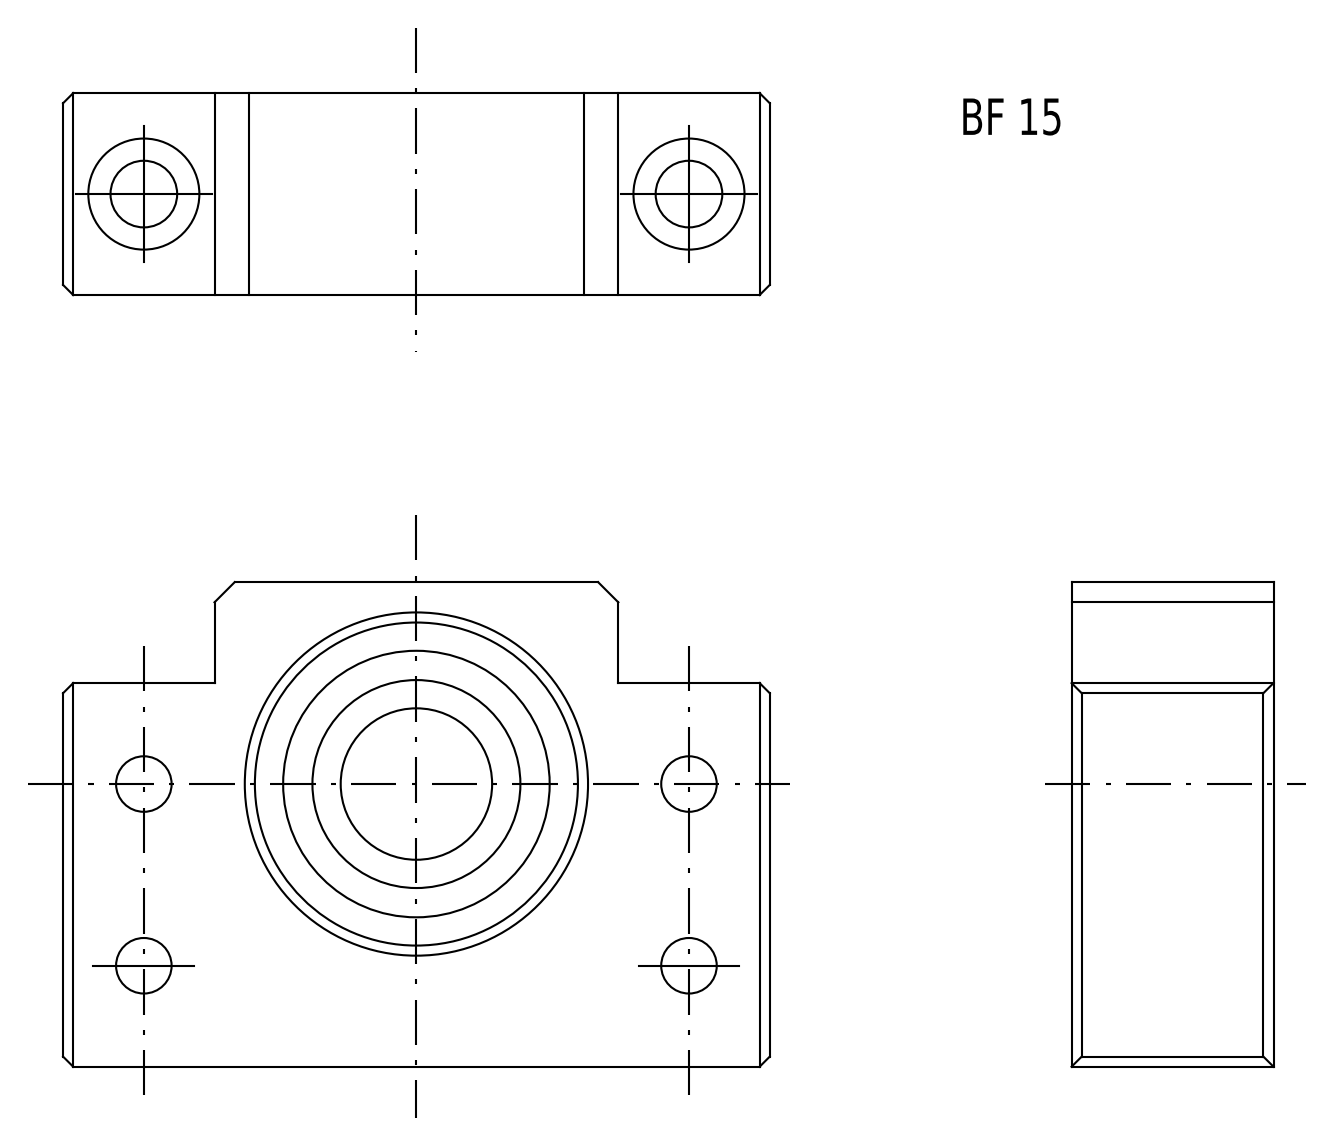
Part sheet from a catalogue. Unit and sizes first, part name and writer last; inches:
Units: inches
Overall size (bounding box): 2.756 × 1.89 × 0.787
Round holes (diameter × count): ⌀0.217 ×4, ⌀0.26 ×2, ⌀0.433 ×2, ⌀0.591 ×1, ⌀0.727 ×1, ⌀0.89 ×1, ⌀1.083 ×1, ⌀1.161 ×1, ⌀1.26 ×1
Round bosses / shafts (diameter × count): ⌀1.016 ×1, ⌀0.774 ×1, ⌀0.711 ×1
Partial cylindrical surfaces — rounded edges, fillets, slot ends (radius × count): R0.075 ×7
Main face-to-face distances: 0.787, 0.24, 0.547, 1.89, 2.756, 0.26, 0.528, 0.02, 0.287, 0.307
Hole centre spacings: 2.126, 0.709, 1.063, 1.278, 2.241
Volume: 2.626 in³ · Surface area: 29.63 in²
Bodies: 13 solids, 295 faces (108 planar, 79 cylindrical, 108 other)
Part name (STEP PRODUCT): BF15組合件
STEP written by: SolidWorks 2008 (CONFIG_CONTROL_DESIGN)
